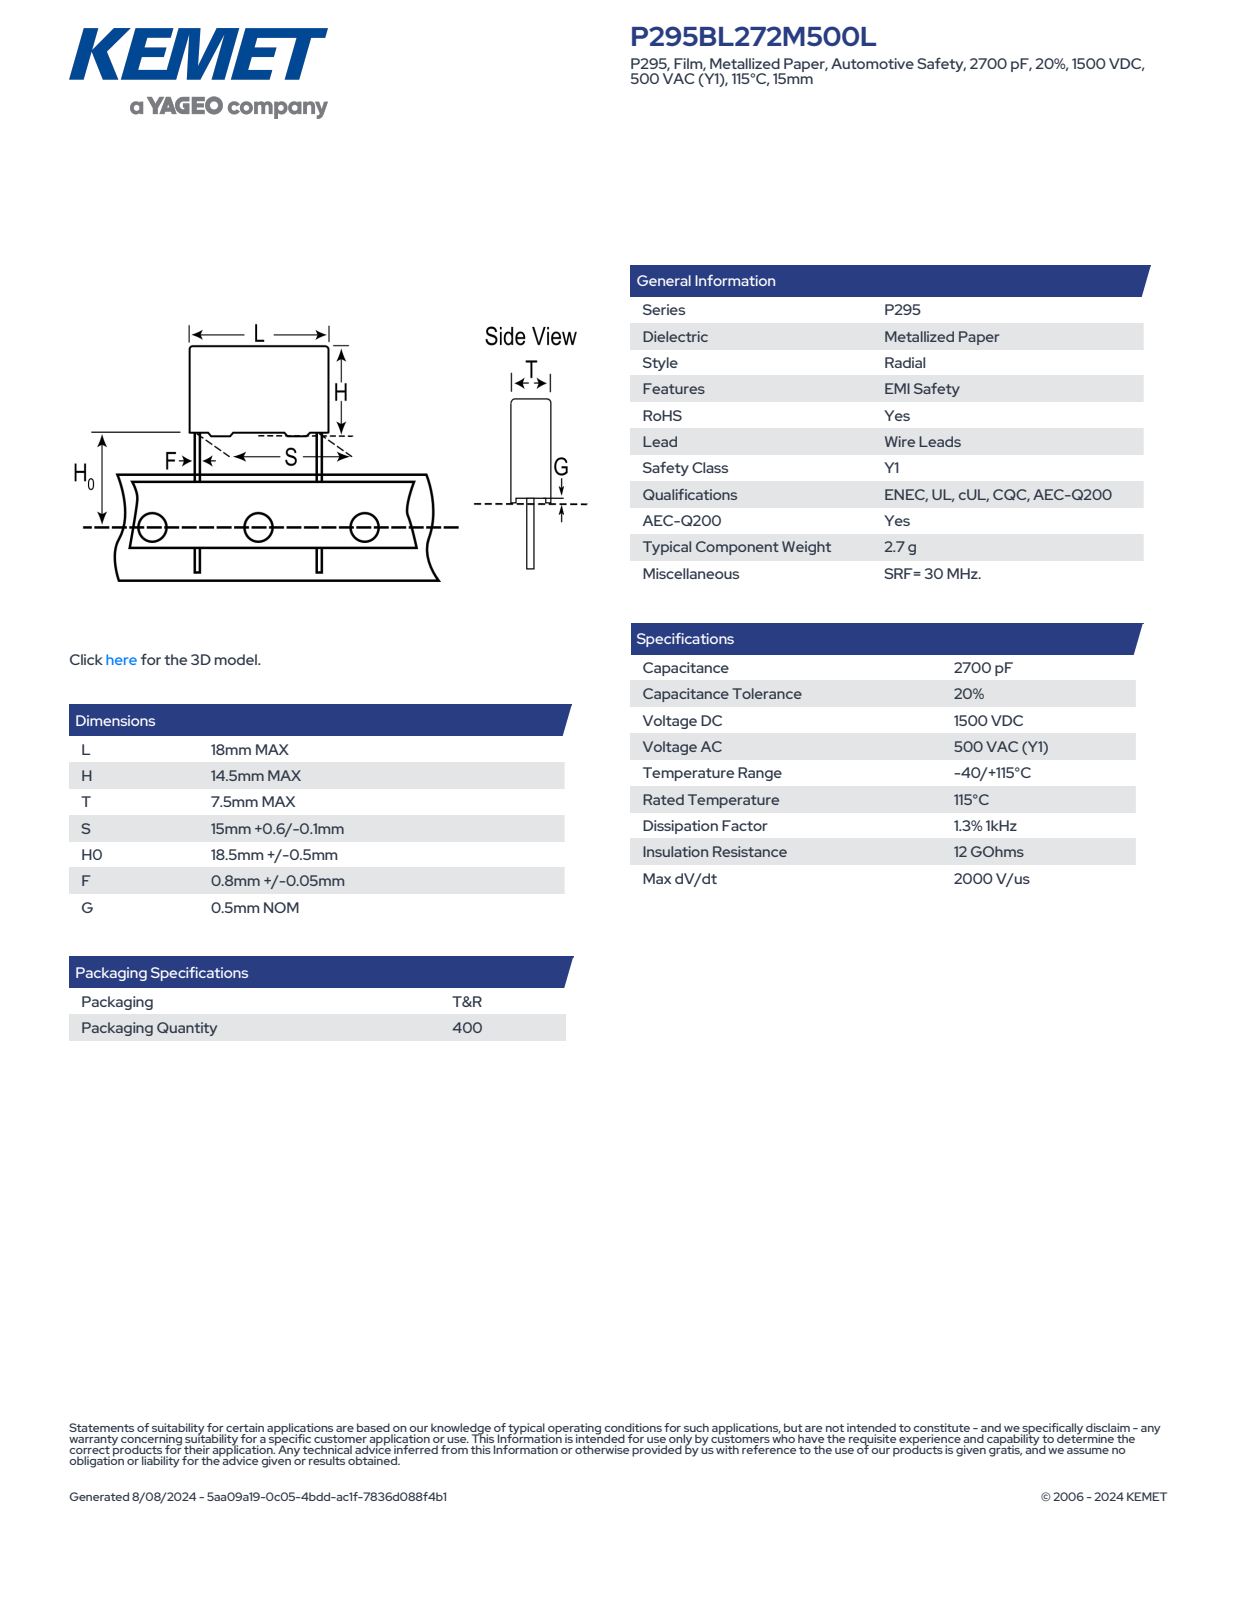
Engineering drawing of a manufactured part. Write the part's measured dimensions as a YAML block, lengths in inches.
part_name: "CFR_RBG_18X14.5X7.5_L18H14.5T7.5S15H019F0.85G0.5"
step_written_by: "SolidWorks 2014 (AUTOMOTIVE_DESIGN)"
units: inches
bodies: {solids: 4, faces: 89, planar: 81, cylindrical: 8, other: 0}
overall_size: [1.319, 0.709, 0.295]
volume: 0.117
surface_area: 1.744
round_bosses_or_shafts:
  - {diameter: 0.033, count: 2}
partial_cylinders:
  - {radius: 0.02, count: 4}
face_to_face_distances: [0.295, 0.551, 0.709, 0.017, 0.278, 0.02, 0.571, 0.261, 0.748, 0.768]
